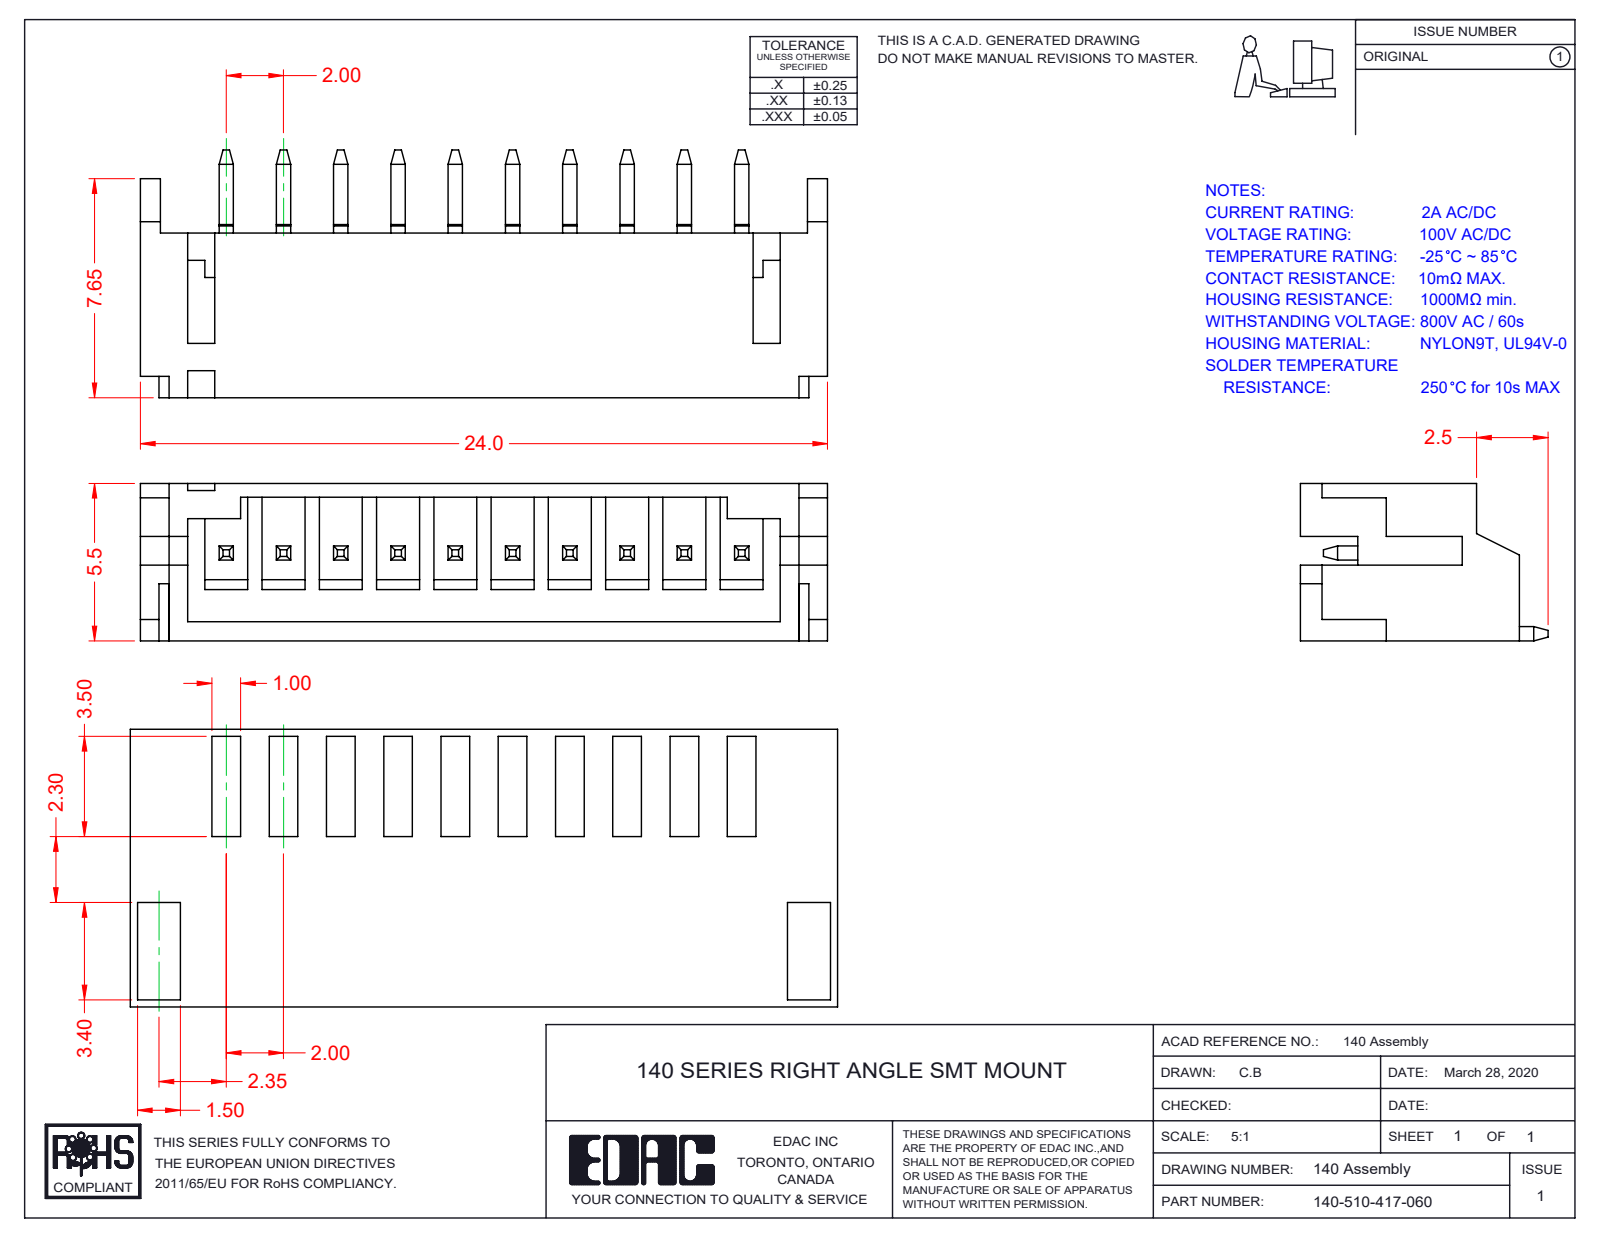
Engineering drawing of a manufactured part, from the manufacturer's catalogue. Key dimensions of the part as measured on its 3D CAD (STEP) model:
Part name (STEP PRODUCT): 140-510-417-060; RA SMT Housing_510; RA SMT Contact; RA SMT Pad
STEP written by: SolidWorks 2016 (CONFIG_CONTROL_DESIGN)
Units: millimetres
Bodies: 13 solids, 540 faces (500 planar, 40 cylindrical, 0 other)
Overall size (bounding box): 24 × 8.65 × 5.5
Volume: 328 mm³ · Surface area: 1 235 mm²
Partial cylindrical surfaces — rounded edges, fillets, slot ends (radius × count): R0.55 ×2
Main face-to-face distances: 5.5, 0.65, 0.67, 4.83, 0.5, 4.35, 5.02, 0.48, 0.95, 1
